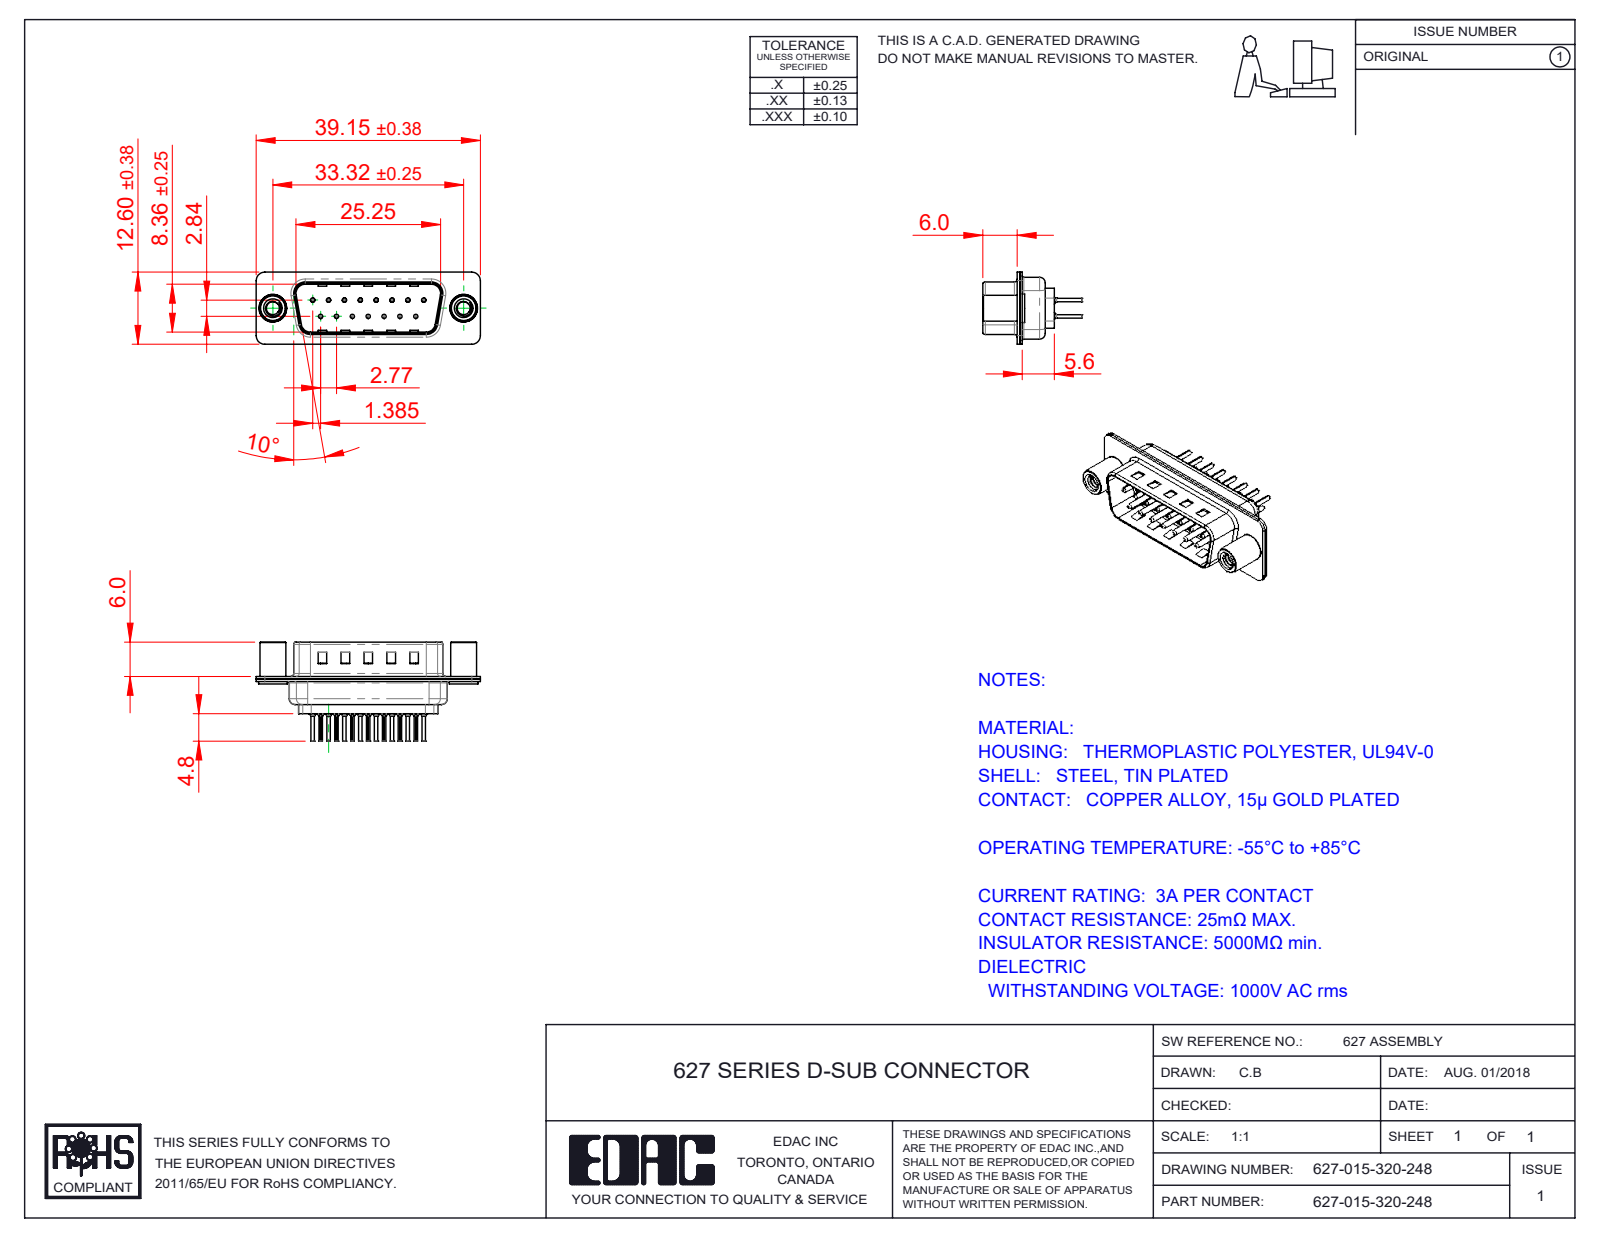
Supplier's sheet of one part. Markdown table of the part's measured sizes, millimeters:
| quantity | value |
| --- | --- |
| part name | 627 Contact Row 1_20L; 627 Housing_15 LP; 627 Shell Front_15 Contacts; 627 Contact Row 2_20L (+3 more) |
| STEP written by | SolidWorks 2020 (CONFIG_CONTROL_DESIGN) |
| units | millimeters |
| bodies | 20 solids, 1844 faces (501 planar, 716 cylindrical, 627 other) |
| overall size | 39.15 × 17.3 × 12.6 |
| volume | 1 894 mm³ |
| surface area | 5 587 mm² |
| round holes (diameter × count) | 0.2 × 15, 0.35 × 15, 1.1 × 15, 1.6 × 15, 2.26 × 2, 4 × 2, 4.8 × 2 |
| round bosses / shafts (diameter × count) | 2 × 15, 1.5 × 15, 0.75 × 15, 0.6 × 15, 5 × 2, 4.9 × 2, 4.5 × 2 |
| partial cylindrical surfaces (radius × count) | 0.1 × 30, 1.5 × 16, 2 × 12, 0.5 × 8, 1.6 × 8, 0.25 × 4, 0.6 × 4, 0.65 × 4 |
| main face-to-face distances | 0.4, 0.45, 0.9, 0.82, 9.58, 8.76, 1.5, 1.4, 6.5, 5.6 |
| hole center spacings | 3.16, 2.77, 5.54, 8.31, 11.08, 5.03, 5.04, 7.48 |
